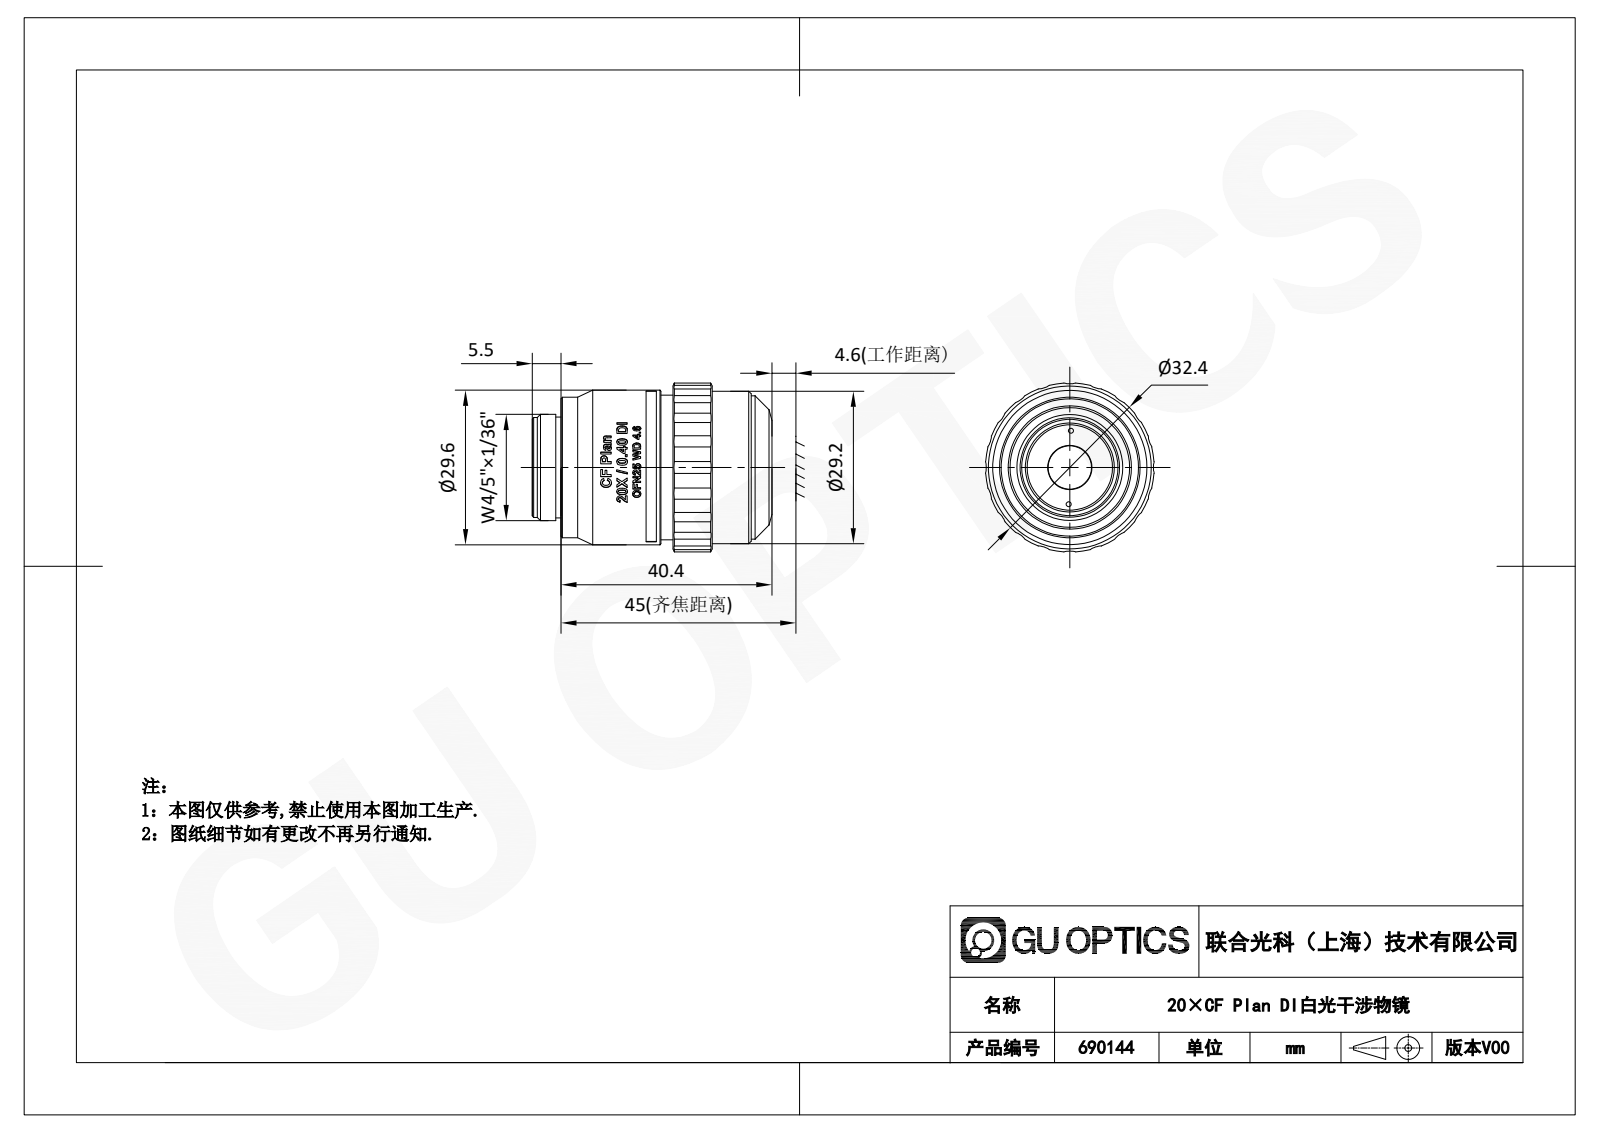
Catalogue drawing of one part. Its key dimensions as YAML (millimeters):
part_name: "X2_5E726D89955C7B52_X0__1; X2_906E51495E3D_X0; X2_59165957_X0__1; X2_5E726D89955C5EA7_X0__2 (+4 more)"
step_written_by: "SolidWorks 2020 (CONFIG_CONTROL_DESIGN)"
units: millimeters
bodies: {solids: 7, faces: 556, planar: 182, cylindrical: 141, other: 233}
overall_size: [45.9, 32.32, 32.32]
volume: 15630
surface_area: 20285
round_holes:
  - {diameter: 1, count: 2}
  - {diameter: 1.57, count: 1}
  - {diameter: 1.73, count: 1}
  - {diameter: 8.3, count: 1}
  - {diameter: 9, count: 1}
  - {diameter: 11, count: 1}
  - {diameter: 11.8, count: 1}
  - {diameter: 12.8, count: 1}
  - {diameter: 15.5, count: 1}
  - {diameter: 15.7, count: 1}
  - {diameter: 16.4, count: 1}
  - {diameter: 16.5, count: 1}
round_bosses_or_shafts:
  - {diameter: 30, count: 1}
  - {diameter: 29.6, count: 1}
  - {diameter: 29.2, count: 1}
  - {diameter: 27.7, count: 1}
  - {diameter: 27.4, count: 1}
  - {diameter: 27, count: 1}
  - {diameter: 26.9, count: 1}
  - {diameter: 26.3, count: 1}
partial_cylinders:
  - {radius: 4, count: 20}
  - {radius: 1.5, count: 4}
  - {radius: 14.7, count: 1}
  - {radius: 16.2, count: 1}
face_to_face_distances: [1.5, 2.5, 5.5, 1.8, 5.1, 11.3, 38.9, 3.7, 2.75, 36]
hole_center_spacings: [7.04, 7.05, 14.1]
